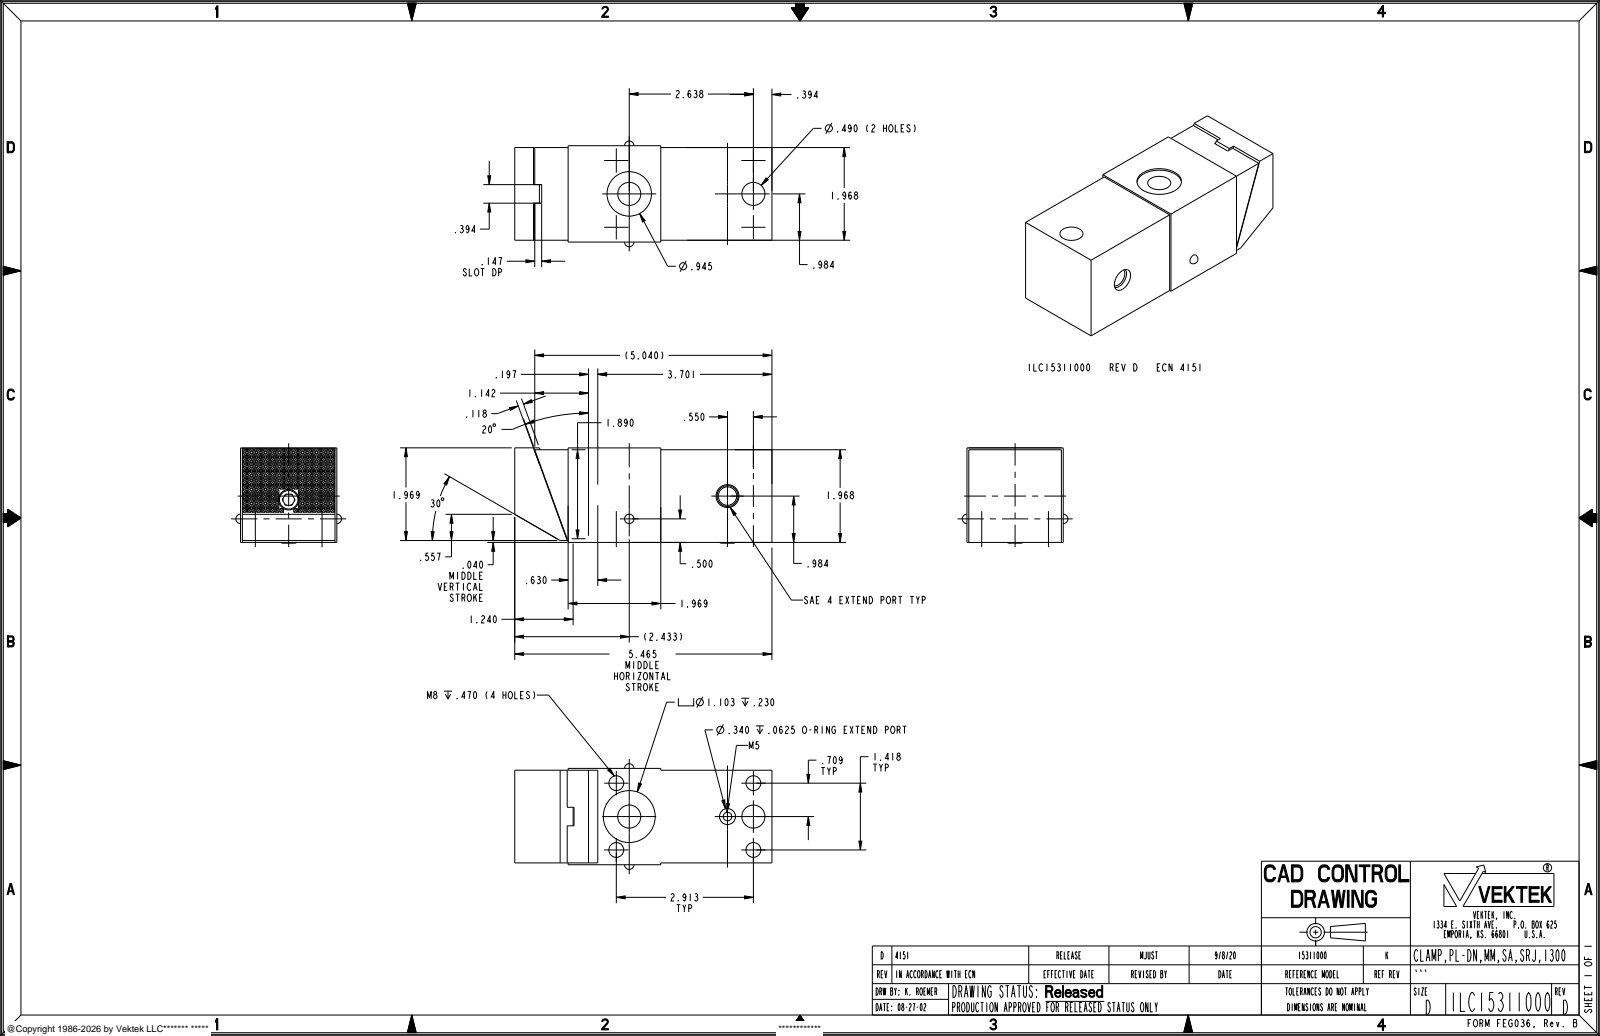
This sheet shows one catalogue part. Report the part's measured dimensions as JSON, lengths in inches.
{"part_name": "ILC15311000", "step_written_by": "PRO/ENGINEER BY PARAMETRIC TECHNOLOGY CORPORATION, 2013320 (AUTOMOTIVE_DESIGN)", "units": "inches", "bodies": {"solids": 2, "faces": 116, "planar": 62, "cylindrical": 30, "other": 24}, "overall_size": [5.472, 2.246, 2.045], "volume_in3": 18.42, "surface_area_in2": 79.87, "round_holes": [[0.315, 4], [0.49, 2], [0.197, 1], [0.244, 1], [0.34, 1], [0.392, 1], [0.433, 1], [0.945, 1], [1.024, 1], [1.103, 1]], "round_bosses_or_shafts": [[0.394, 1]], "face_to_face_distances": [0.039, 1.968, 2.007, 2.007, 1.968, 2.046, 3.701, 0.207, 3.908, 1.564], "hole_center_spacings": [0.709, 0.761, 0.897, 1.418, 2.467, 2.731, 2.913, 2.998]}
